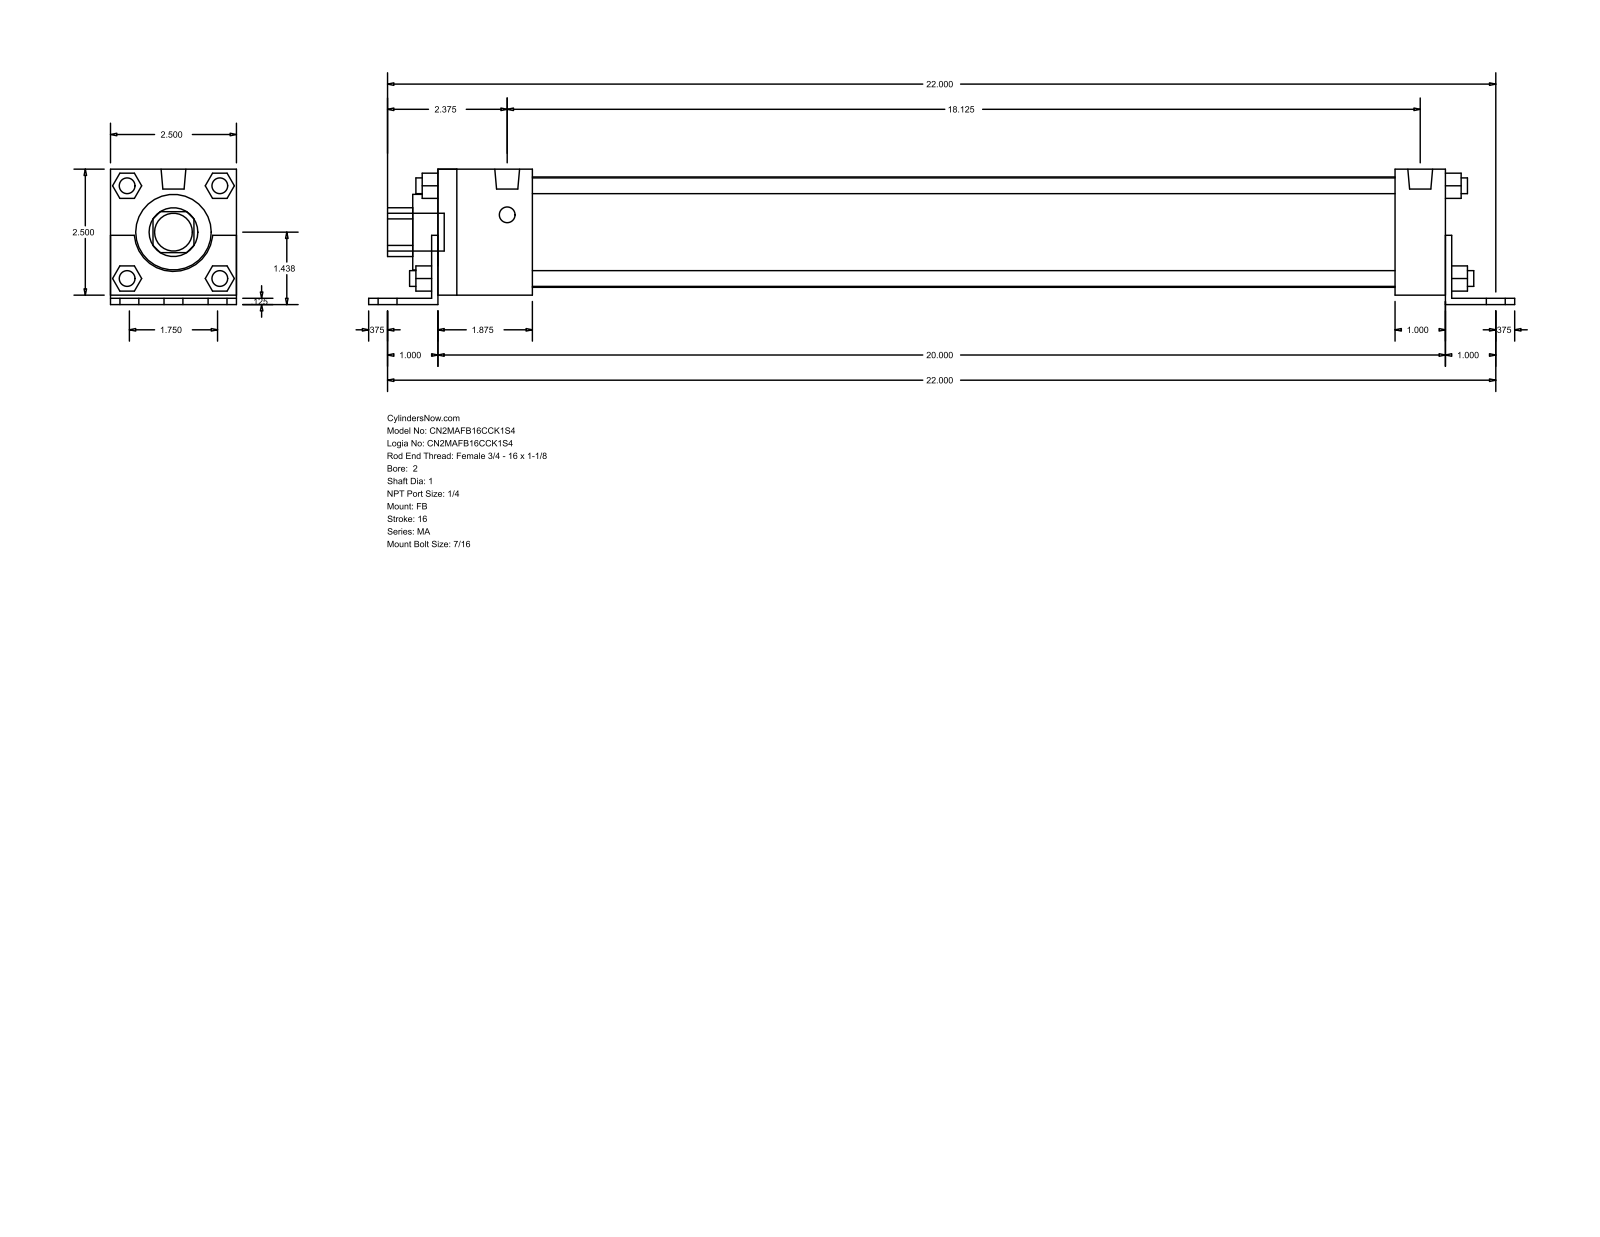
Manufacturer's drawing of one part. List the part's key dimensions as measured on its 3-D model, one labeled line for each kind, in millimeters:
Part name (STEP PRODUCT): MA_FB__0200_1
STEP written by: GSSL Pune (CONFIG_CONTROL_DESIGN)
Units: millimetres
Bodies: 0 solids, 140 faces (105 planar, 35 cylindrical, 0 other)
Overall size (bounding box): 577.85 × 68.26 × 63.5
Round holes (diameter × count): ⌀25.4 ×1, ⌀38.1 ×1, ⌀55.63 ×1
Round bosses / shafts (diameter × count): ⌀7.94 ×8, ⌀11.11 ×6, ⌀12.49 ×2, ⌀19.05 ×1
Partial cylindrical surfaces — rounded edges, fillets, slot ends (radius × count): R12.29 ×1, R19.81 ×1
Main face-to-face distances: 63.5, 3.17, 4.76, 68.26, 1.59, 65.09, 12.7, 3.18, 508, 511.18
